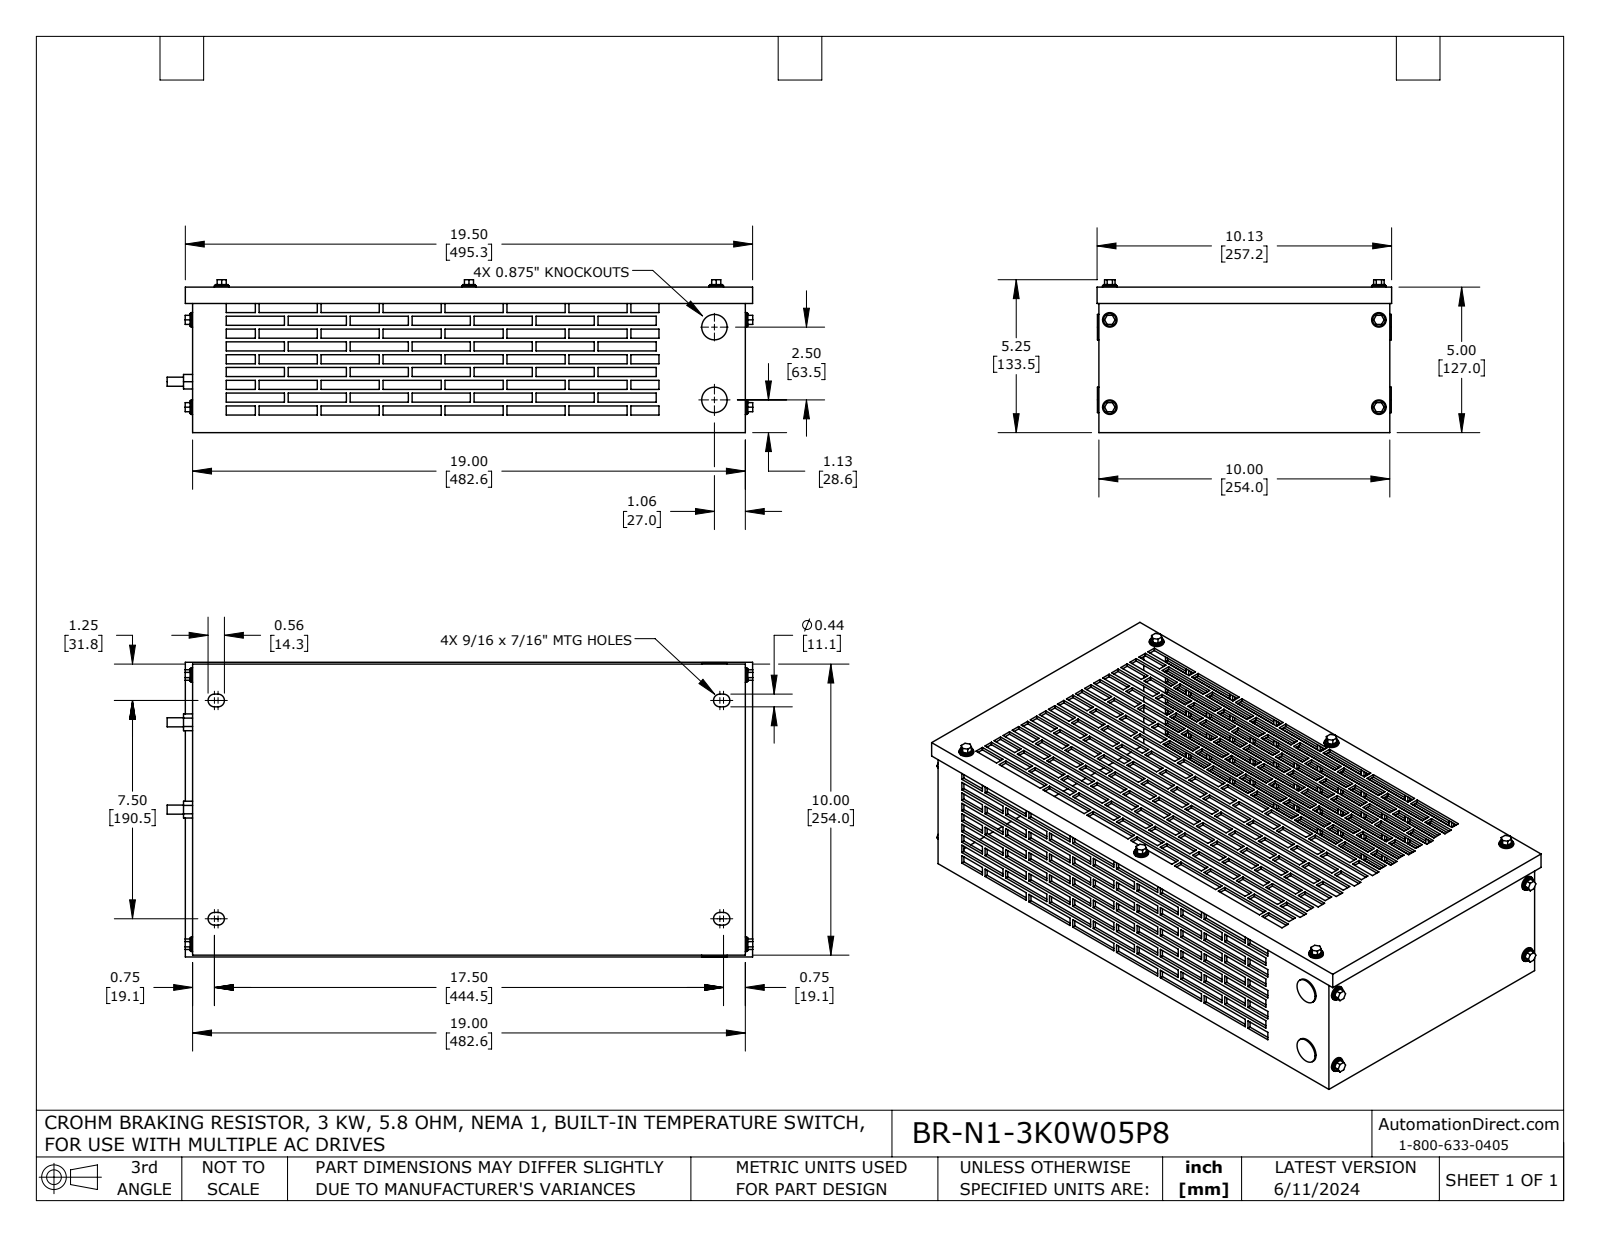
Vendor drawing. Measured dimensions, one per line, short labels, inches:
name: BR-N1-3K0W05P8
written by: SolidWorks 2021 (AUTOMOTIVE_DESIGN)
unit: in
bodies: 35 solids, 1454 faces (1342 planar, 112 cylindrical, 0 other)
size: 20.129 × 10.125 × 5.254
volume: 51.07 in³; area: 1 155 in²
holes: 10× ⌀0.25, 2× ⌀0.75
bosses: 10× ⌀0.5, 10× ⌀0.437, 2× ⌀0.875, 2× ⌀0.313
rounds: 8× R0.219
face distances: 0.1, 4.9, 5, 4.8, 18.9, 9.9, 10, 19, 18.8, 9.8
hole spacings: 9.25, 8.5, 12.562, 3, 9.724, 17, 19.354, 2.5
